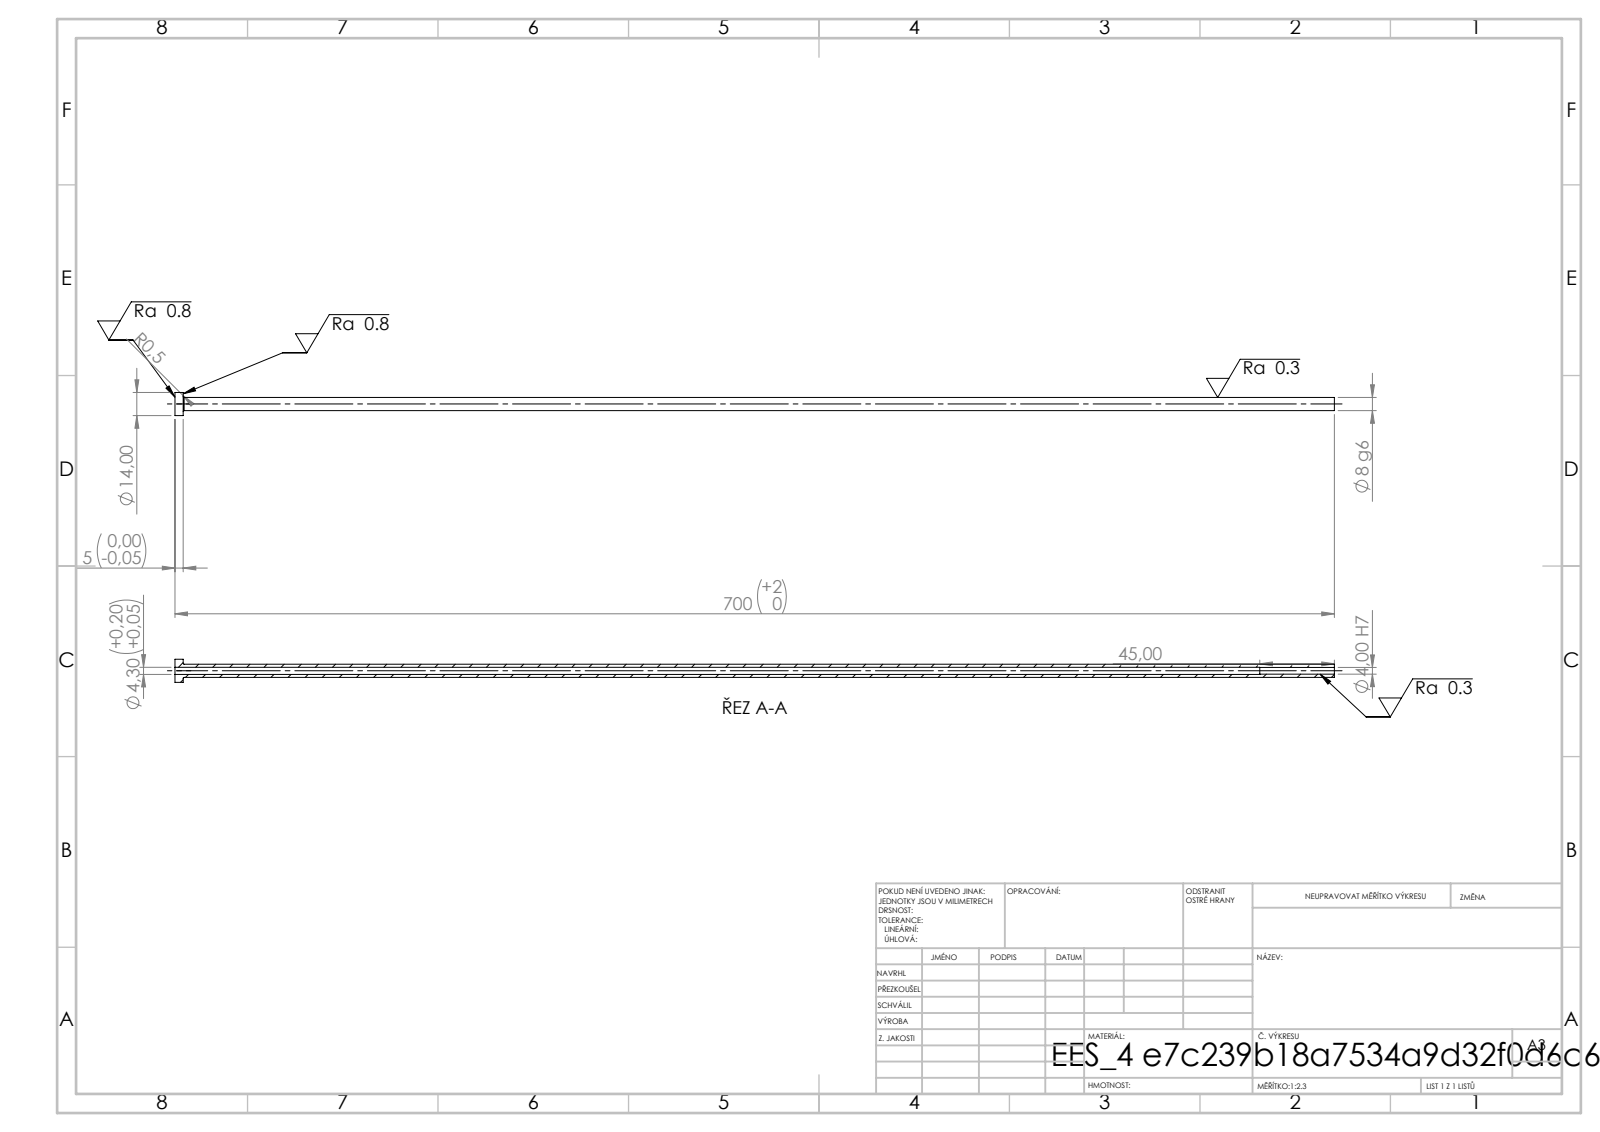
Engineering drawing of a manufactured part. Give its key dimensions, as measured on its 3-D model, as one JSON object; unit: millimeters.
{"step_written_by": "SolidWorks 2019 (CONFIG_CONTROL_DESIGN)", "units": "millimeters", "bodies": {"solids": 1, "faces": 14, "planar": 4, "cylindrical": 8, "other": 2}, "overall_size": [700, 14, 14], "volume_mm3": 25628, "surface_area_mm2": 27378, "round_holes": [[4, 1], [4.3, 1]], "round_bosses_or_shafts": [[14, 1], [8, 1]], "face_to_face_distances": [5, 700, 695, 655, 650, 45]}
